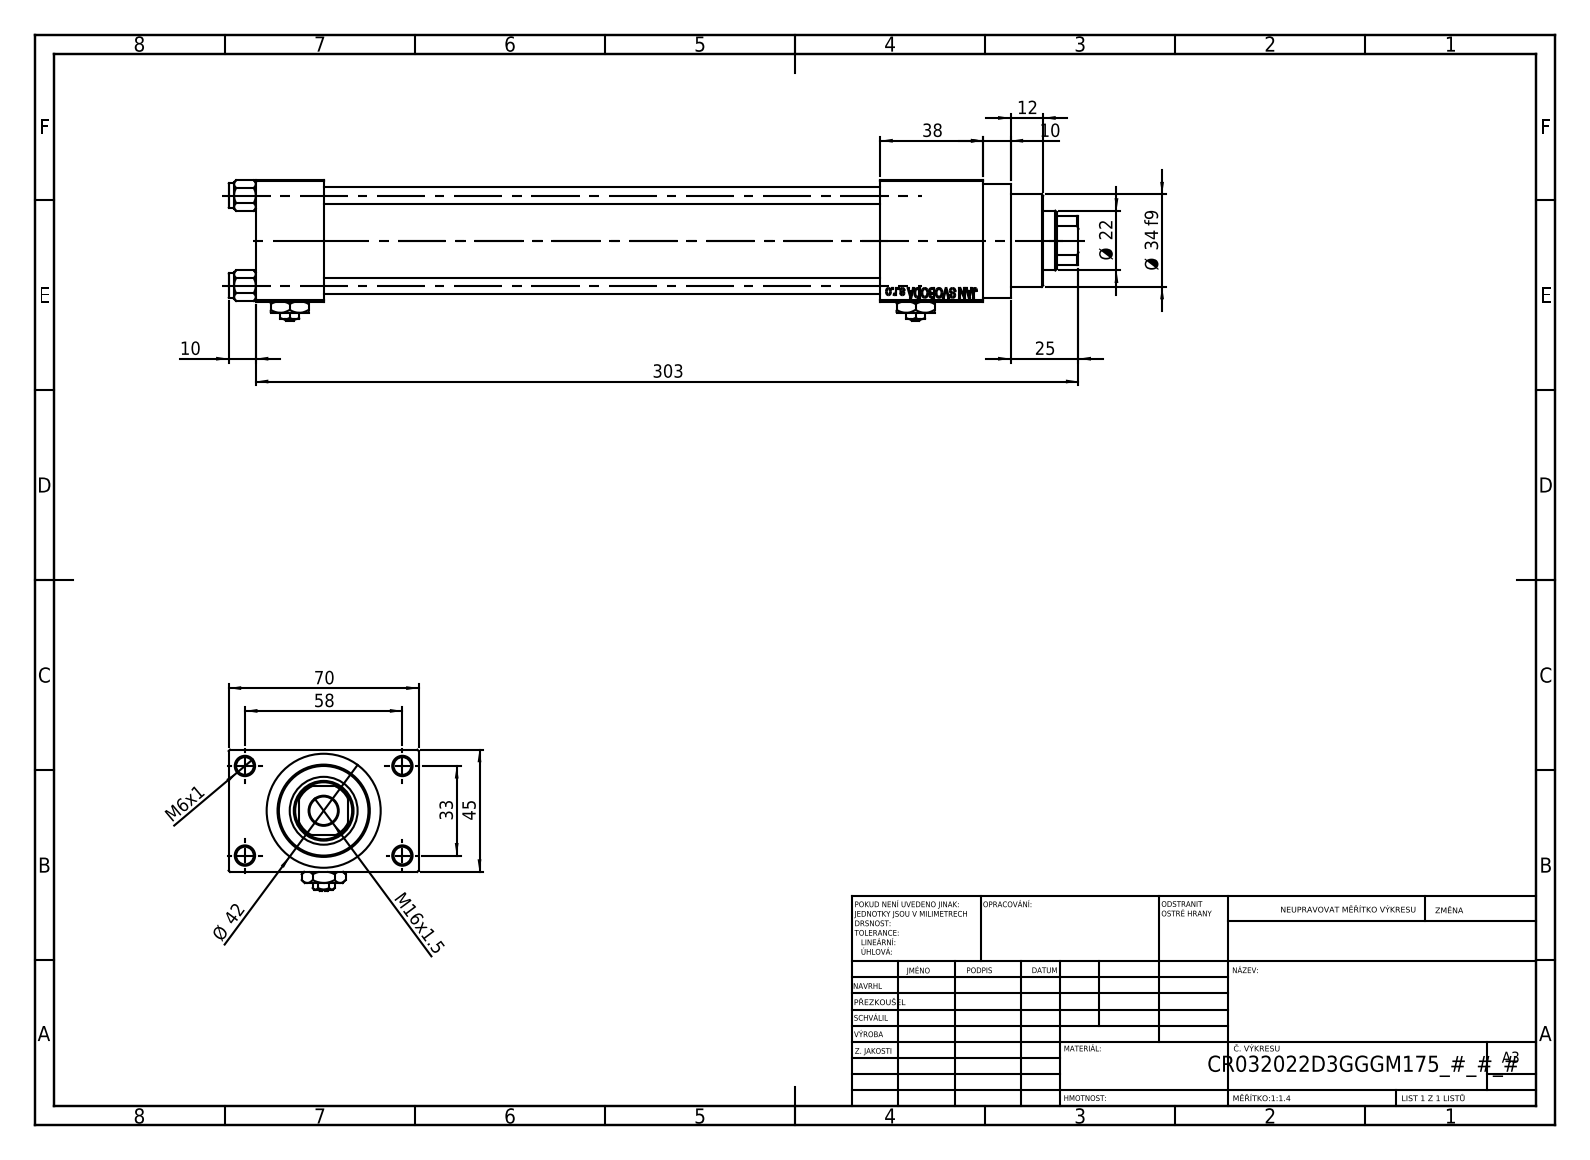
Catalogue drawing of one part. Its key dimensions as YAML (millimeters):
part_name: "Zatka_pro_OIL_PORT; V215CR_D_Body; NUT_M5_D; V215CR_D_TYCINKA (+2 more)"
step_written_by: "SolidWorks 2019 (CONFIG_CONTROL_DESIGN)"
units: millimeters
bodies: {solids: 13, faces: 1202, planar: 542, cylindrical: 100, other: 560}
overall_size: [313, 70, 52]
volume: 370947
surface_area: 137686
round_holes:
  - {diameter: 6, count: 4}
  - {diameter: 6.5, count: 4}
  - {diameter: 7, count: 2}
  - {diameter: 13.16, count: 2}
  - {diameter: 20, count: 2}
  - {diameter: 10.5, count: 1}
  - {diameter: 22, count: 1}
  - {diameter: 24, count: 1}
  - {diameter: 25, count: 1}
  - {diameter: 32, count: 1}
  - {diameter: 33, count: 1}
round_bosses_or_shafts:
  - {diameter: 9, count: 4}
  - {diameter: 42, count: 1}
  - {diameter: 38, count: 1}
  - {diameter: 34, count: 1}
partial_cylinders:
  - {radius: 10.5, count: 1}
face_to_face_distances: [45, 25, 12.5, 57.5, 205, 230, 243, 38, 70, 268]
hole_center_spacings: [12.4, 23.48, 33.2, 33.37, 35.35, 45.6, 56.35, 33]
